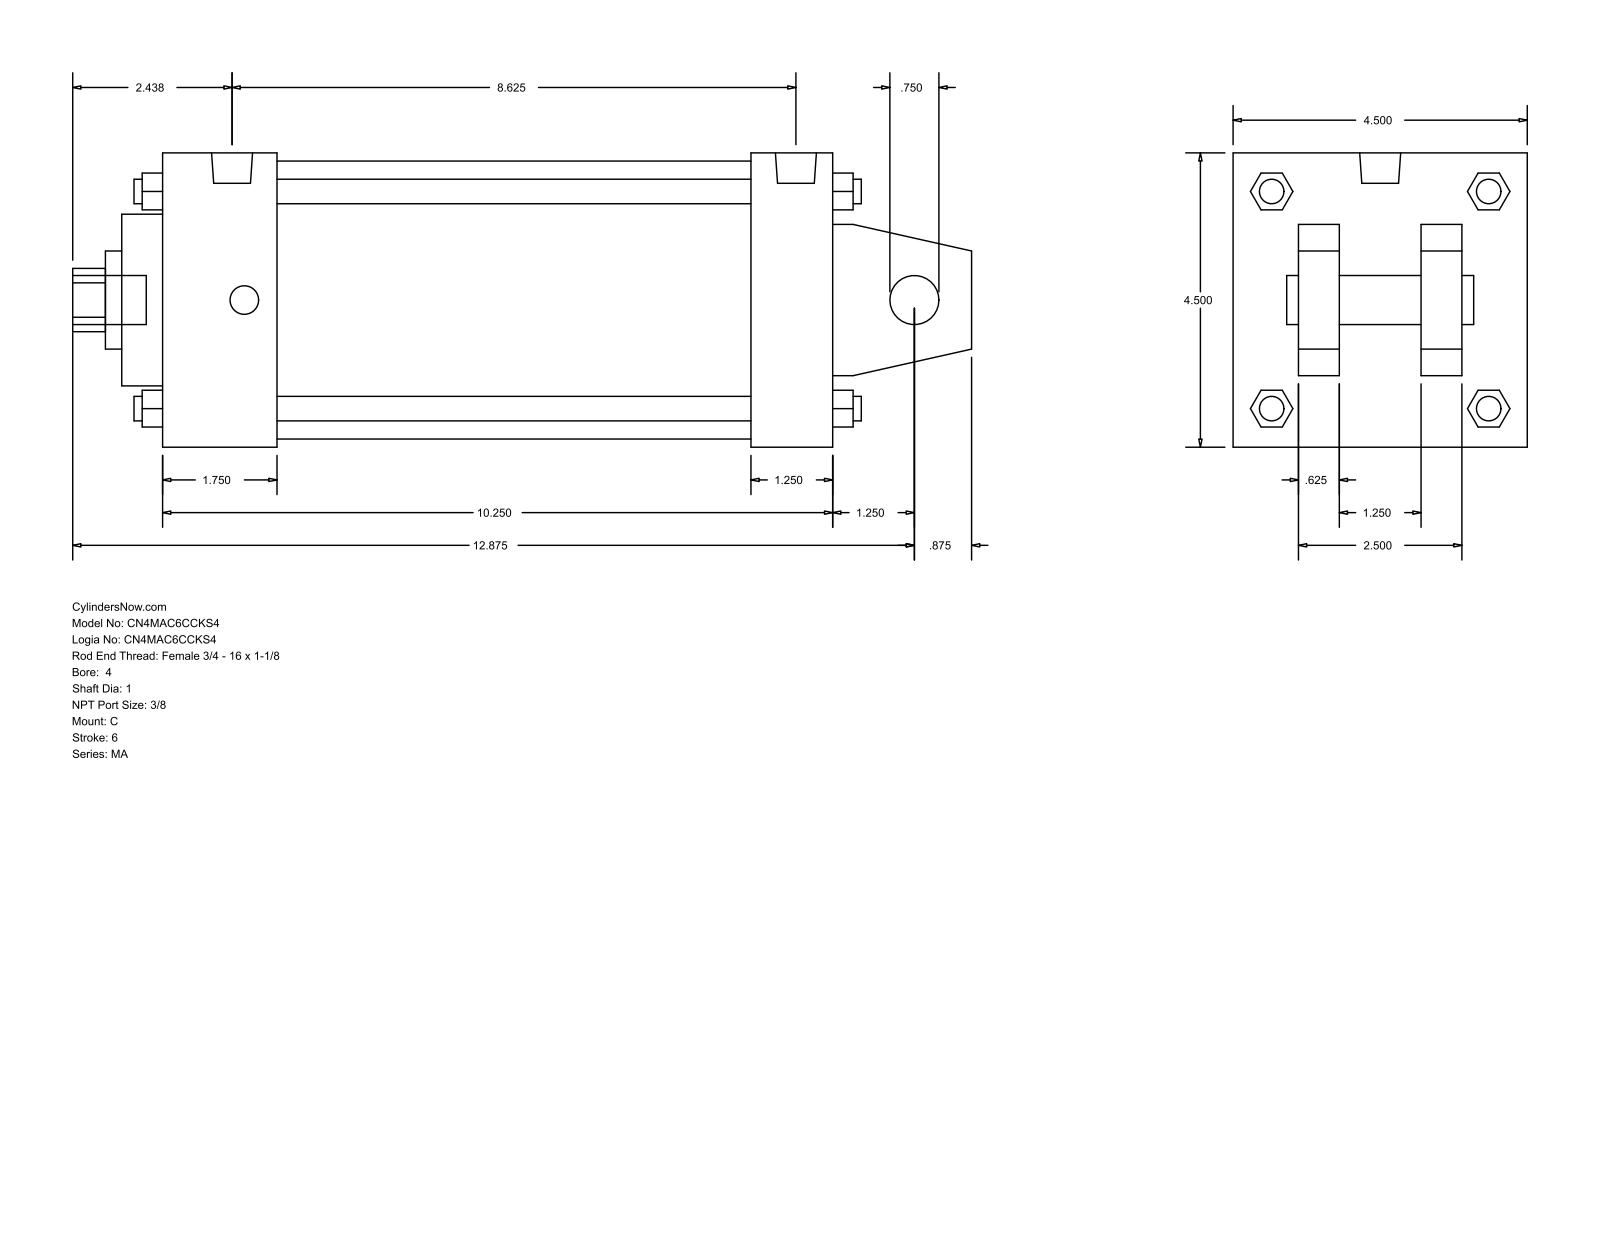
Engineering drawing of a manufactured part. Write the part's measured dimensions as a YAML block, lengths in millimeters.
part_name: "MA_C__0400_1"
step_written_by: "GSSL Pune (CONFIG_CONTROL_DESIGN)"
units: millimeters
bodies: {solids: 0, faces: 141, planar: 109, cylindrical: 32, other: 0}
overall_size: [349.25, 114.3, 114.3]
round_holes:
  - {diameter: 19.05, count: 1}
  - {diameter: 25.4, count: 1}
  - {diameter: 38.1, count: 1}
  - {diameter: 66.67, count: 1}
  - {diameter: 107.95, count: 1}
round_bosses_or_shafts:
  - {diameter: 11.11, count: 4}
  - {diameter: 9.53, count: 4}
  - {diameter: 15.93, count: 2}
  - {diameter: 19.05, count: 1}
partial_cylinders:
  - {radius: 12.29, count: 1}
face_to_face_distances: [114.3, 260.35, 15.87, 73.03, 41.27, 25.4, 88.9, 47.63, 228.6, 31.75]
